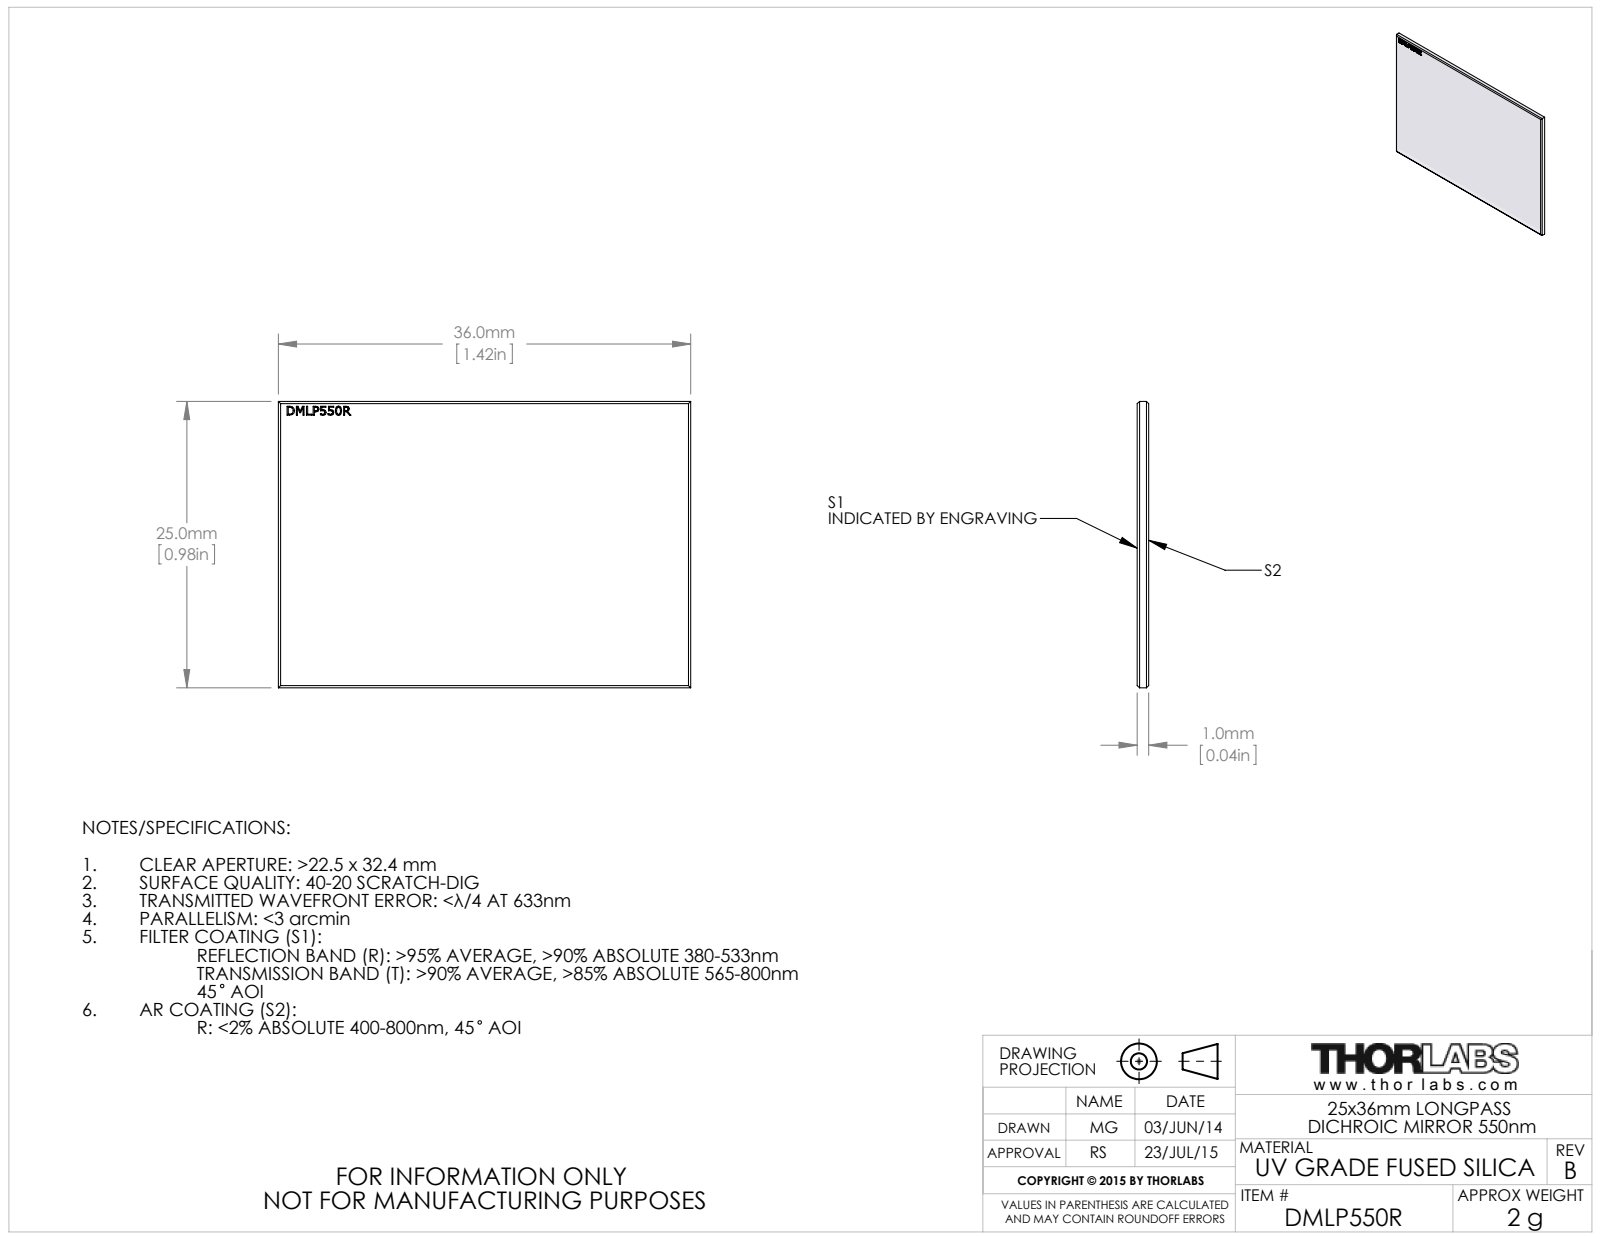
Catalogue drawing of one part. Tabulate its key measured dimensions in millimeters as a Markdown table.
| quantity | value |
| --- | --- |
| part name | TTN028311-E0W |
| STEP written by | SolidWorks 2012 (CONFIG_CONTROL_DESIGN) |
| units | millimeters |
| bodies | 1 solid, 143 faces (84 planar, 0 cylindrical, 59 other) |
| overall size | 36 × 25 × 1 |
| volume | 895 mm³ |
| surface area | 1 893 mm² |
| main face-to-face distances | 1, 25, 18.1, 36, 25.88, 0.9, 0.68, 24.57, 0.43, 0.59 |
